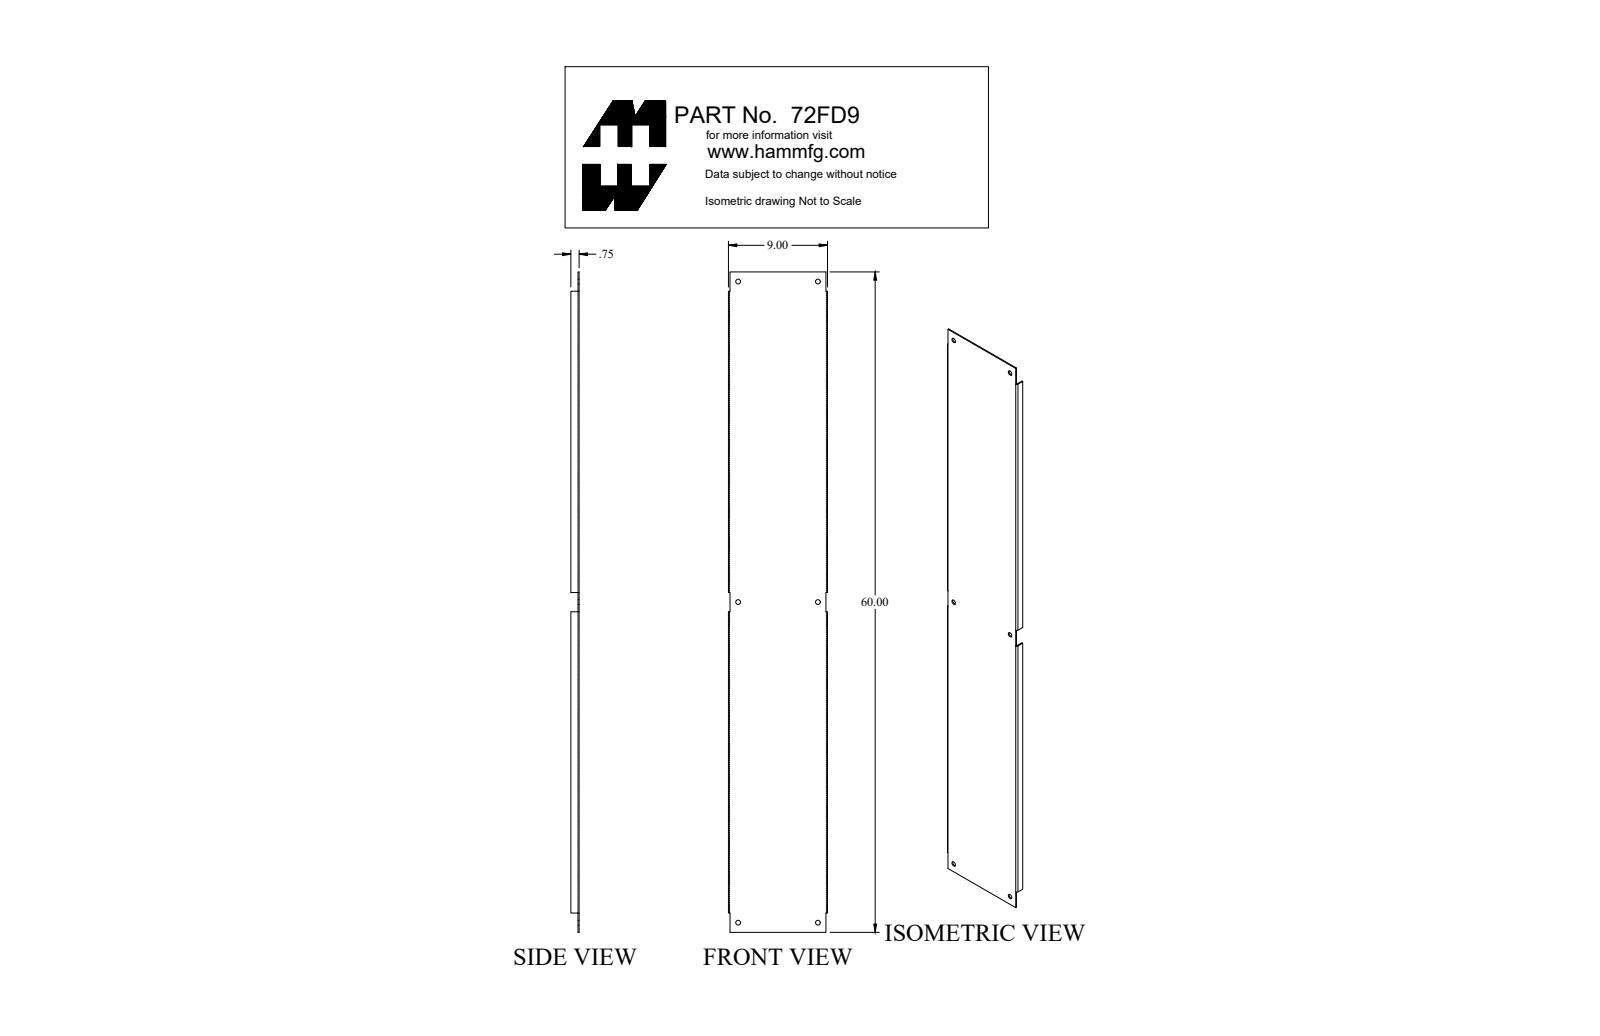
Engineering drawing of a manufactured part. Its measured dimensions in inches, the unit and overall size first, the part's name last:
Units: inches
Overall size (bounding box): 60 × 9 × 0.75
Round holes (diameter × count): ⌀0.437 ×6
Partial cylindrical surfaces — rounded edges, fillets, slot ends (radius × count): R0.048 ×2, R0.143 ×2
Main face-to-face distances: 0.095, 8.905, 8.81, 9, 0.75, 0.655, 0.143, 8.857, 0.048, 8.762
Hole centre spacings: 29.125, 30.014, 7.25, 58.25, 58.699
Volume: 57.46 in³ · Surface area: 1 224 in²
Bodies: 1 solid, 50 faces (30 planar, 20 cylindrical, 0 other)
Part name (STEP PRODUCT): 72FD9_Default
STEP written by: SolidWorks 2018 (CONFIG_CONTROL_DESIGN)
